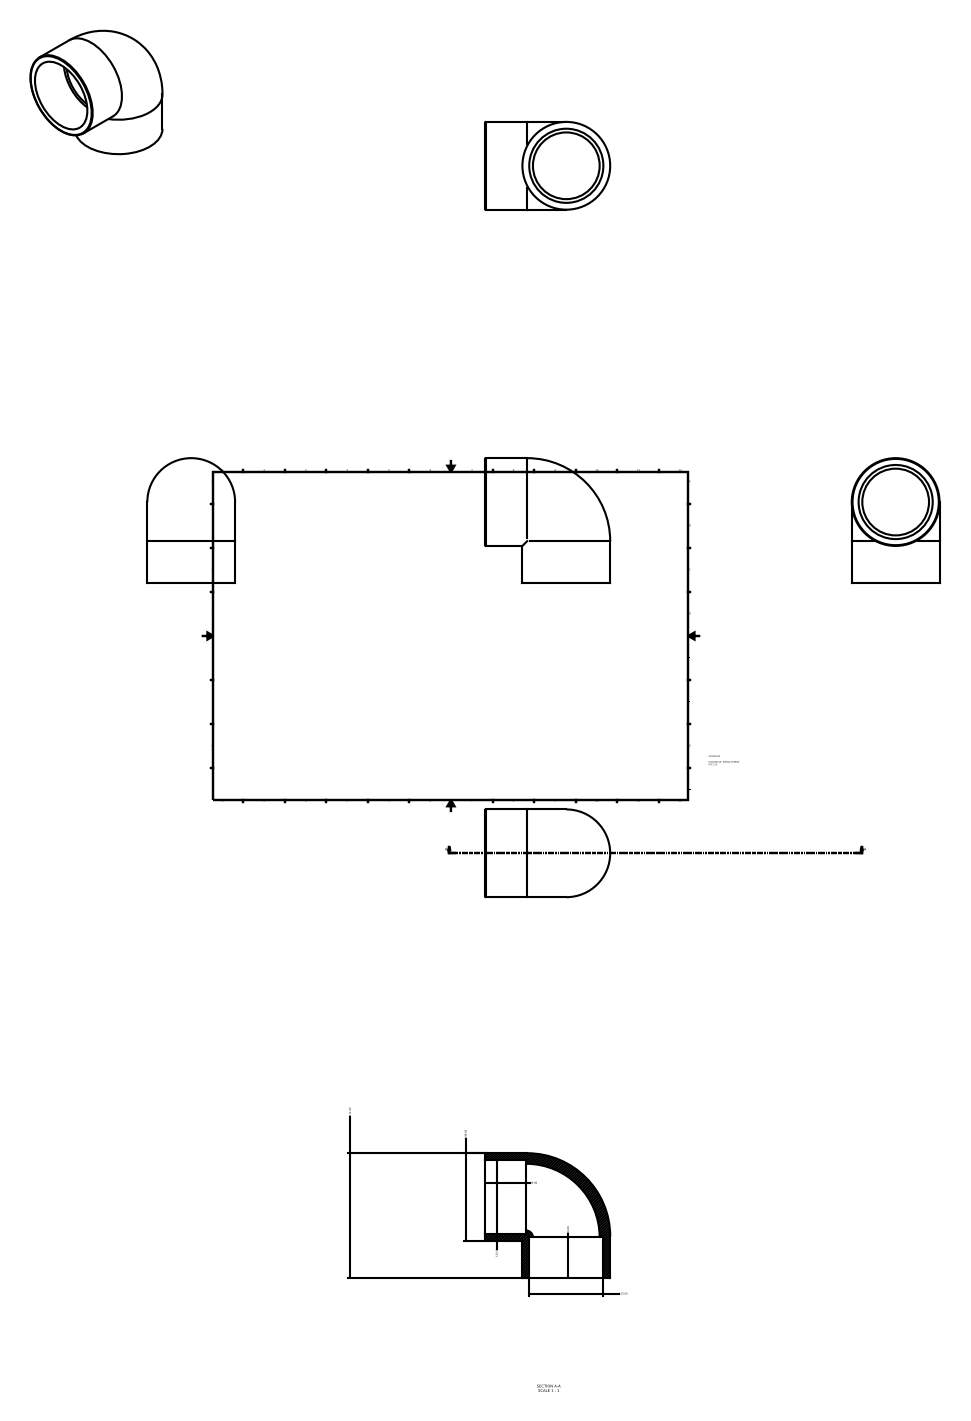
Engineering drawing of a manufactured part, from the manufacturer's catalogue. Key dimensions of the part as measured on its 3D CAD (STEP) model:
Part name (STEP PRODUCT): 050500125
STEP written by: Autodesk Inventor 2015 (AUTOMOTIVE_DESIGN)
Units: millimetres
Bodies: 1 solid, 11 faces (4 planar, 4 cylindrical, 3 other)
Overall size (bounding box): 211 × 211 × 148
Volume: 1 489 000 mm³ · Surface area: 220 379 mm²
Round holes (diameter × count): ⌀125 ×2
Round bosses / shafts (diameter × count): ⌀148 ×2
Main face-to-face distances: 69
